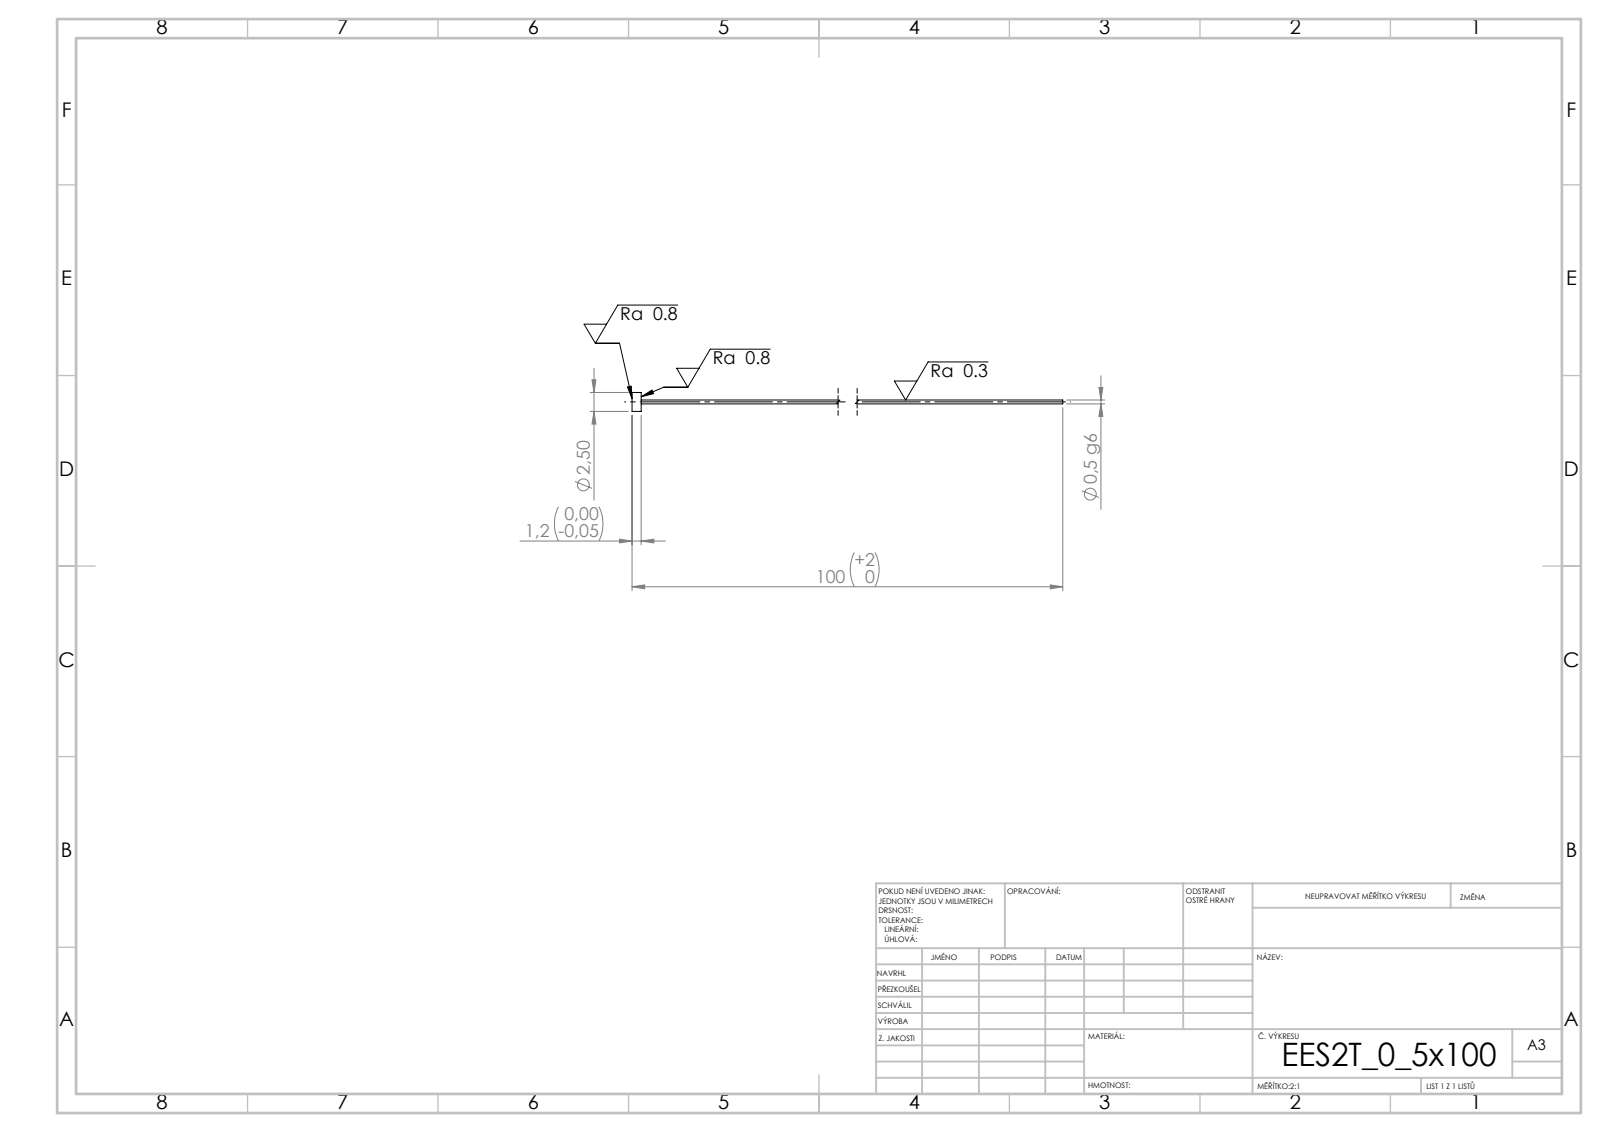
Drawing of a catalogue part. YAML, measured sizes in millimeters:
step_written_by: "SolidWorks 2019 (CONFIG_CONTROL_DESIGN)"
units: millimeters
bodies: {solids: 1, faces: 7, planar: 3, cylindrical: 4, other: 0}
overall_size: [100, 2.5, 2.5]
volume: 25
surface_area: 174
round_bosses_or_shafts:
  - {diameter: 2.5, count: 1}
  - {diameter: 0.5, count: 1}
face_to_face_distances: [1.2, 100, 98.8]
